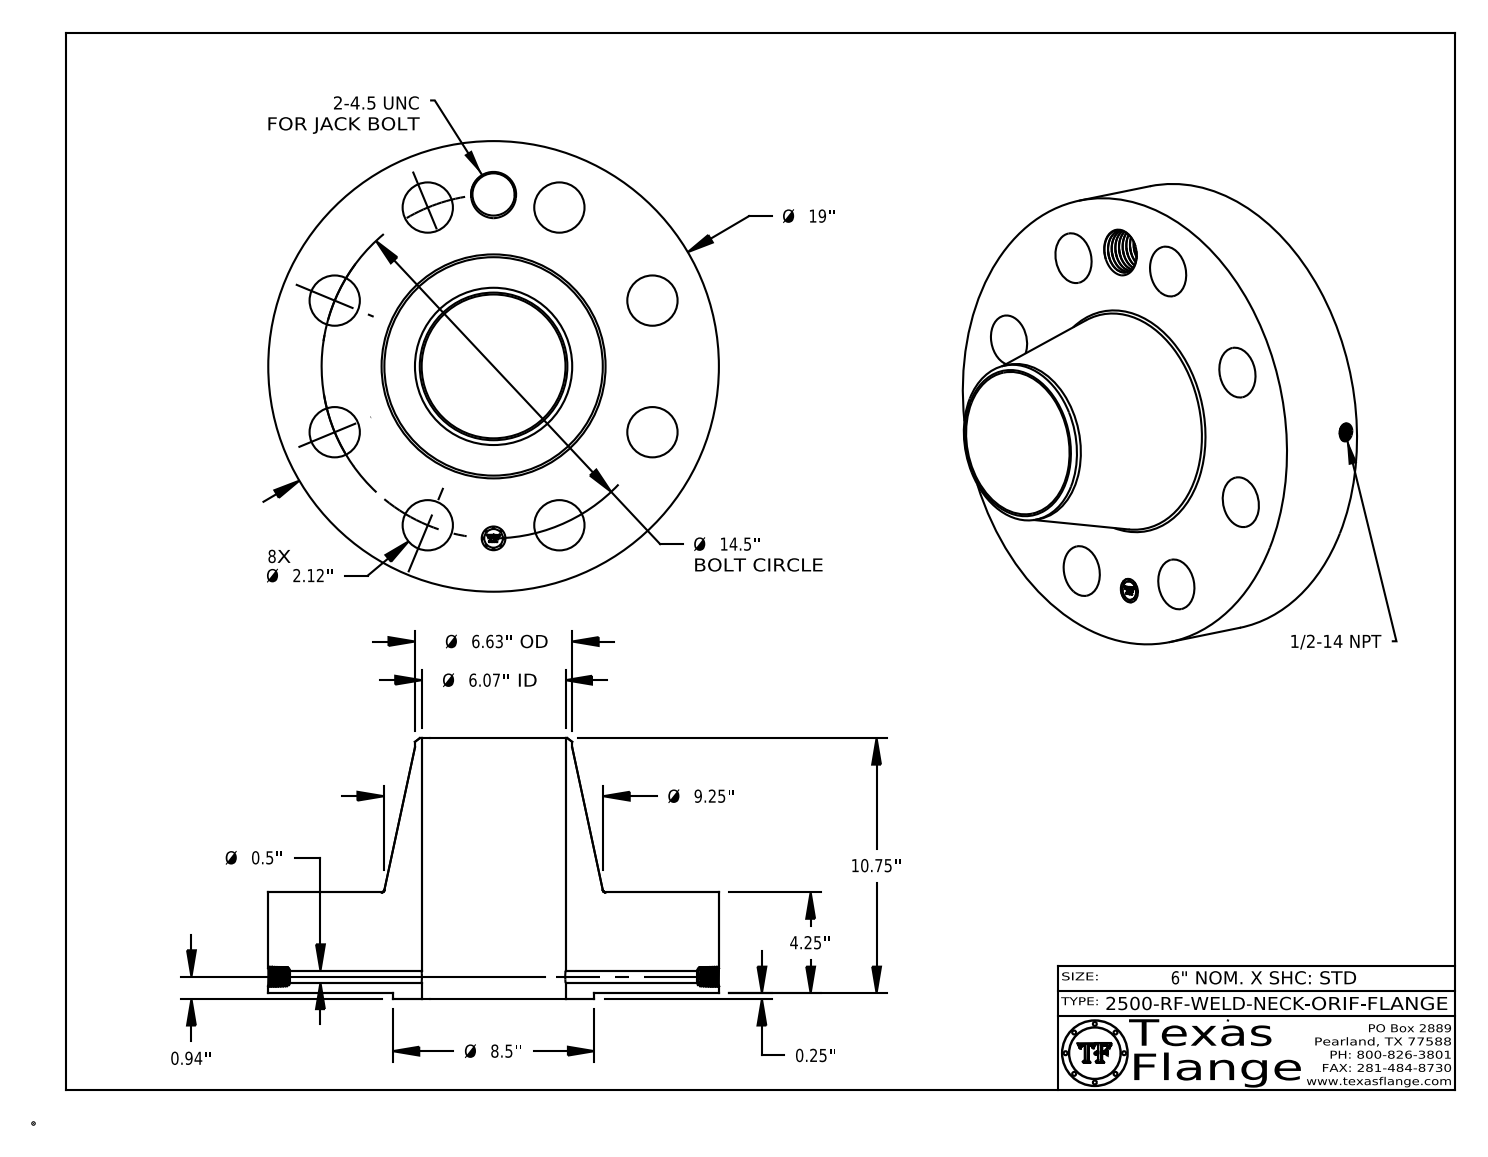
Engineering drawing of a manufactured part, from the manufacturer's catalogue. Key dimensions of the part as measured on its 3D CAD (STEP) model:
Part name (STEP PRODUCT): 2500-RF-WELD-NECK
STEP written by: CATIA V5 STEP AP214 (AUTOMOTIVE_DESIGN)
Units: inches
Bodies: 1 solid, 794 faces (369 planar, 102 cylindrical, 323 other)
Overall size (bounding box): 19 × 19 × 11
Volume: 1 085 in³ · Surface area: 1 331 in²
Round holes (diameter × count): ⌀2.12 ×8, ⌀0.5 ×1, ⌀0.672 ×1, ⌀1 ×1, ⌀1.781 ×1, ⌀6.065 ×1
Round bosses / shafts (diameter × count): ⌀0.061 ×8, ⌀19 ×1, ⌀8.5 ×1, ⌀6.63 ×1, ⌀0.788 ×1
Main face-to-face distances: 4.25, 0.25, 4.5, 11, 10.75, 6.5, 4.485, 4.235, 0.015, 6.515
Hole centre spacings: 7.25, 5.549, 10.253, 13.396, 2.829, 8.056, 12.056, 14.221
